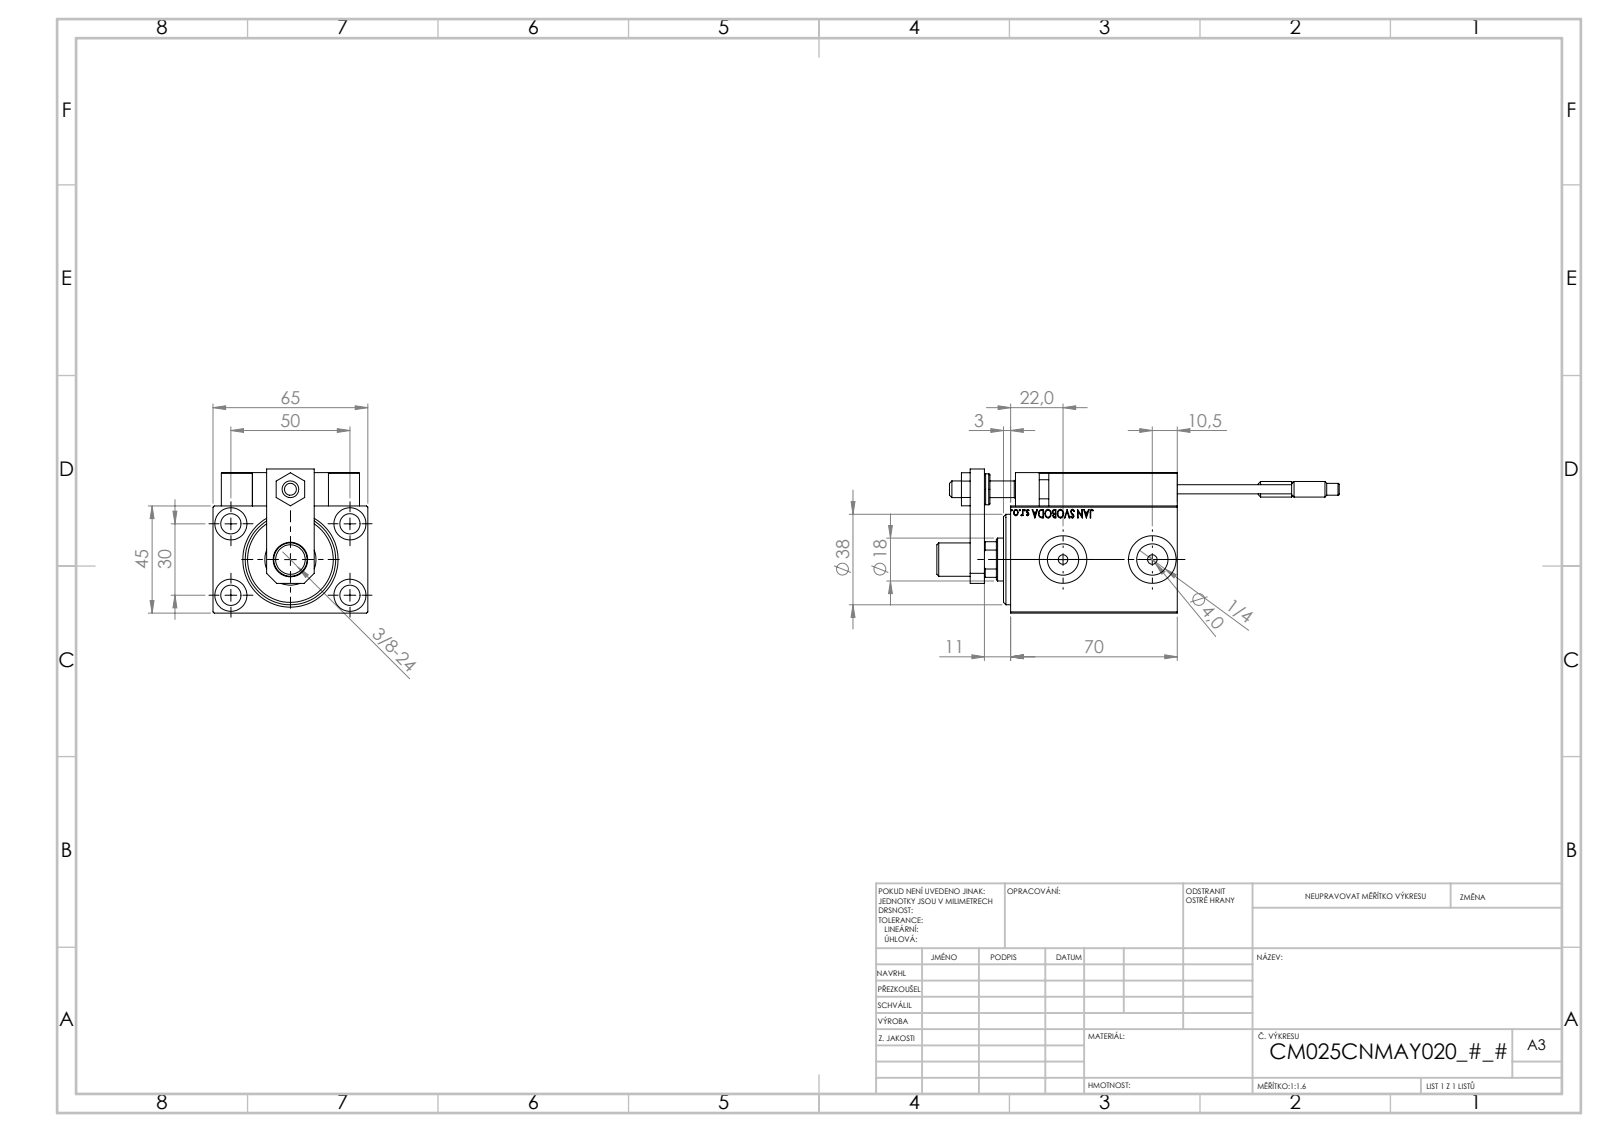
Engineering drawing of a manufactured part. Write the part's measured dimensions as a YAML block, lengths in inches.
part_name: "ALLEN BOLT D8; KONCOVKA_Y; V450CM_C_VCP; MAGNET (+7 more)"
step_written_by: "SolidWorks 2019 (CONFIG_CONTROL_DESIGN)"
units: inches
bodies: {solids: 24, faces: 1317, planar: 565, cylindrical: 200, other: 552}
overall_size: [6.654, 2.559, 2.382]
volume: 13.86
surface_area: 110.3
round_holes:
  - {diameter: 0.157, count: 6}
  - {diameter: 0.315, count: 5}
  - {diameter: 0.335, count: 5}
  - {diameter: 0.126, count: 4}
  - {diameter: 0.531, count: 4}
  - {diameter: 0.197, count: 2}
  - {diameter: 0.518, count: 2}
  - {diameter: 0.787, count: 2}
  - {diameter: 0.276, count: 1}
  - {diameter: 0.571, count: 1}
  - {diameter: 0.709, count: 1}
  - {diameter: 0.846, count: 1}
round_bosses_or_shafts:
  - {diameter: 0.197, count: 4}
  - {diameter: 0.256, count: 2}
  - {diameter: 0.15, count: 2}
  - {diameter: 0.551, count: 1}
  - {diameter: 0.512, count: 1}
  - {diameter: 0.472, count: 1}
  - {diameter: 0.433, count: 1}
partial_cylinders:
  - {radius: 0.012, count: 30}
  - {radius: 0.118, count: 2}
  - {radius: 0.335, count: 1}
face_to_face_distances: [1.772, 2.323, 0.551, 2.559, 0.236, 0.118, 0.748, 0.197, 0.276, 0.787]
hole_center_spacings: [1.148, 0.448, 0.787, 0.87, 1.138, 1.165, 1.169, 1.181]
